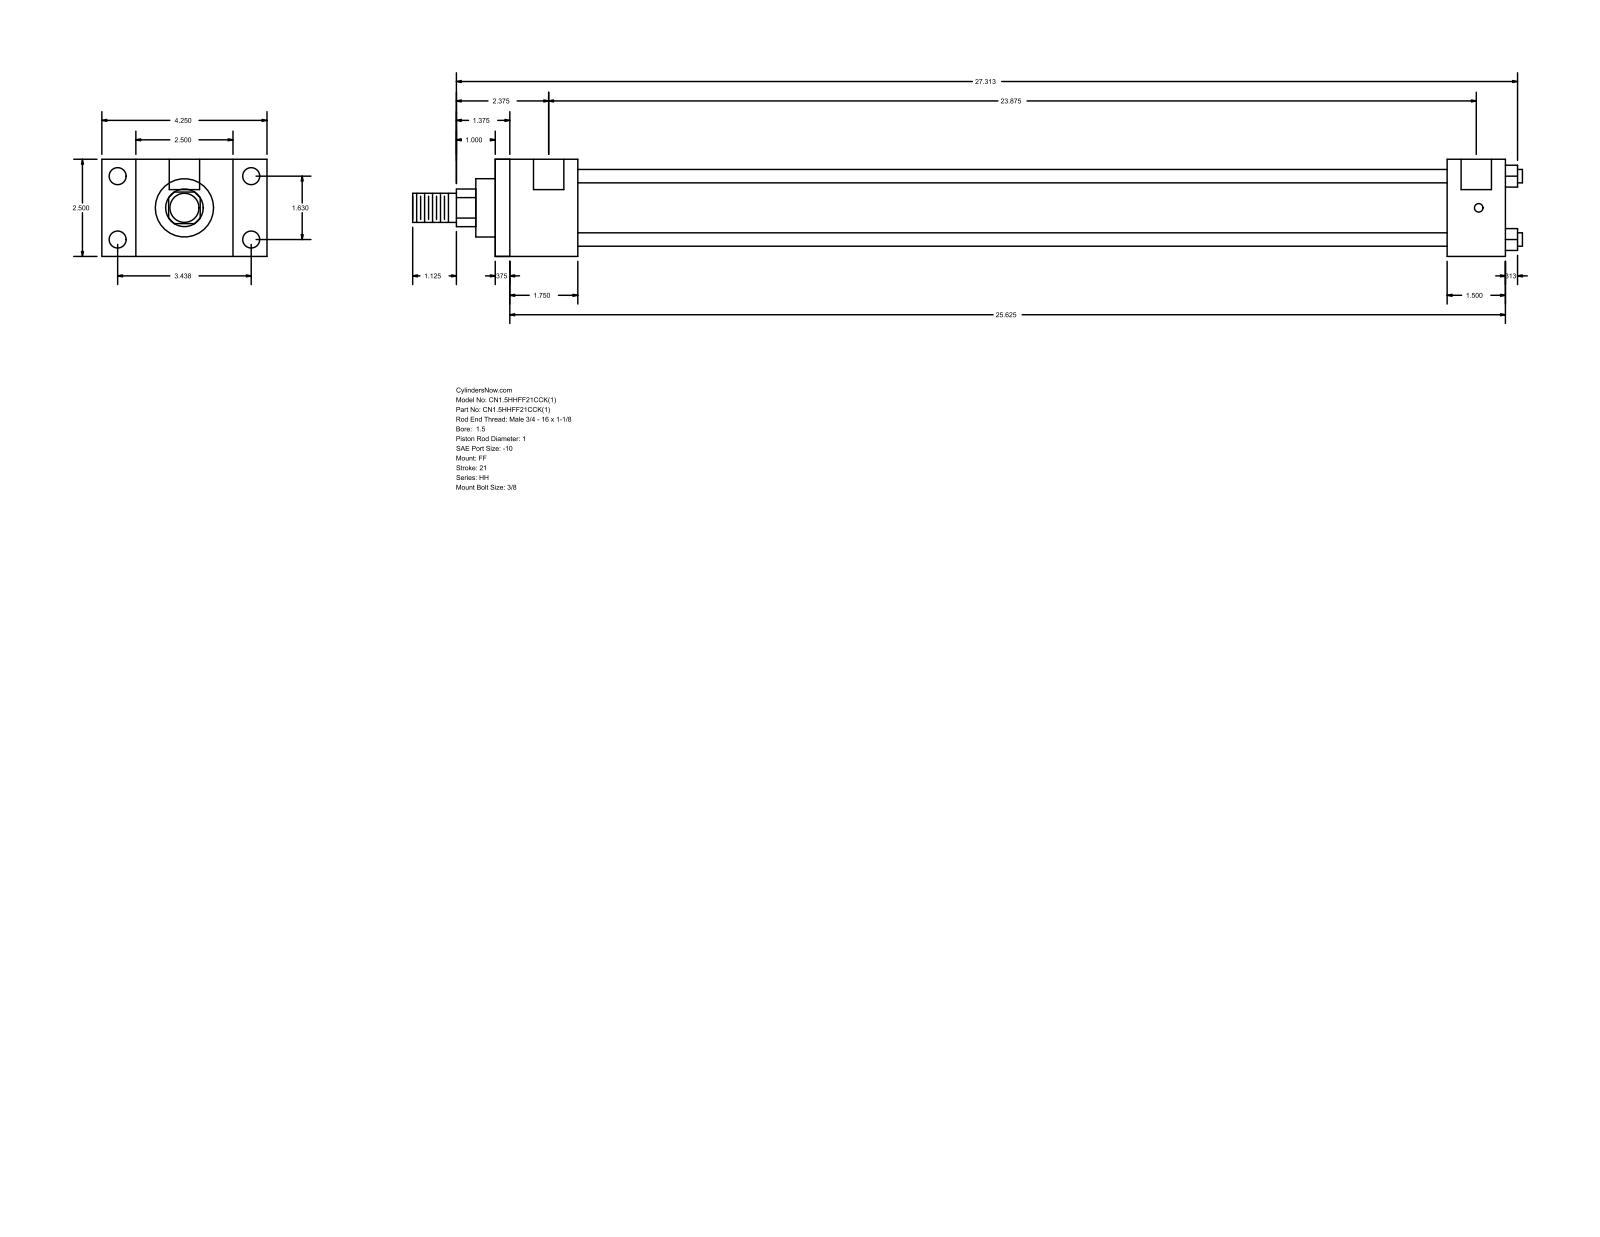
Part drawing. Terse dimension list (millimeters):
name: HH_FF__0150_1
written by: GSSL Pune (CONFIG_CONTROL_DESIGN)
unit: mm
bodies: 0 solids, 92 faces (64 planar, 28 cylindrical, 0 other)
size: 725.49 × 107.95 × 63.5
holes: 4× ⌀5.56, 4× ⌀11.13, 2× ⌀19.84
bosses: 4× ⌀8.76, 1× ⌀44.45, 1× ⌀38.1, 1× ⌀25.4, 1× ⌀19.05
rounds: 1× R12.29
face distances: 63.5, 660.4, 9.52, 650.88, 38.1, 53.98, 44.46, 606.42, 622.3, 612.78
hole spacings: 1.59, 41.4, 87.32, 96.64, 608.01, 609.6, 606.42
